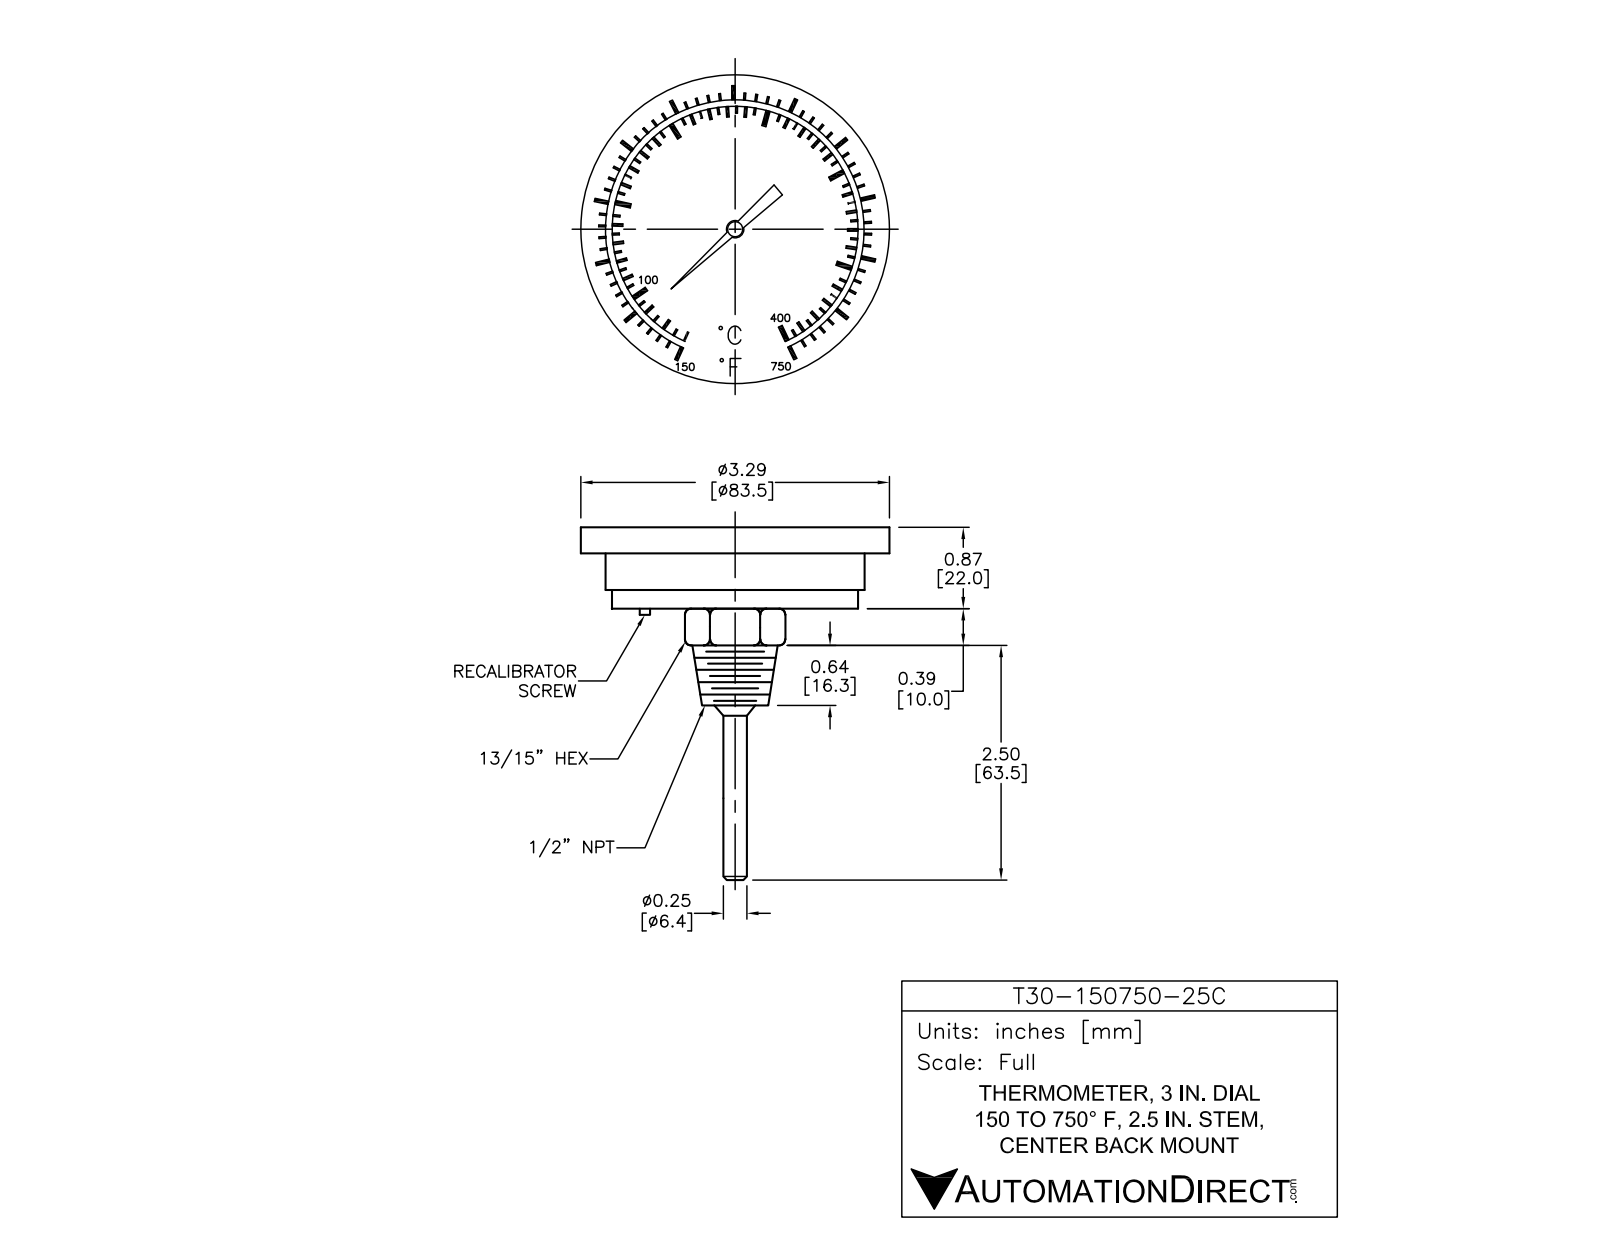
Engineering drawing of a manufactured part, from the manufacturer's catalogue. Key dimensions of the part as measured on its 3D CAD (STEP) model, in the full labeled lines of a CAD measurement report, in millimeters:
Part name (STEP PRODUCT): T30-150750-25C
STEP written by: SolidWorks 2021 (CONFIG_CONTROL_DESIGN)
Units: millimetres
Bodies: 58 solids, 944 faces (735 planar, 124 cylindrical, 85 other)
Overall size (bounding box): 133.6 × 83.6 × 83.6
Volume: 51 620 mm³ · Surface area: 21 990 mm²
Round holes (diameter × count): ⌀1.7 ×1, ⌀68.3 ×1
Round bosses / shafts (diameter × count): ⌀83.6 ×1, ⌀70.1 ×1, ⌀66.5 ×1, ⌀21.5 ×1, ⌀6.6 ×1
Partial cylindrical surfaces — rounded edges, fillets, slot ends (radius × count): R1 ×1, R21.8 ×1, R24.6 ×1
Main face-to-face distances: 5.6, 2, 7.6, 22.1, 16.5, 14.5, 7.4, 15, 9.3, 7.1
